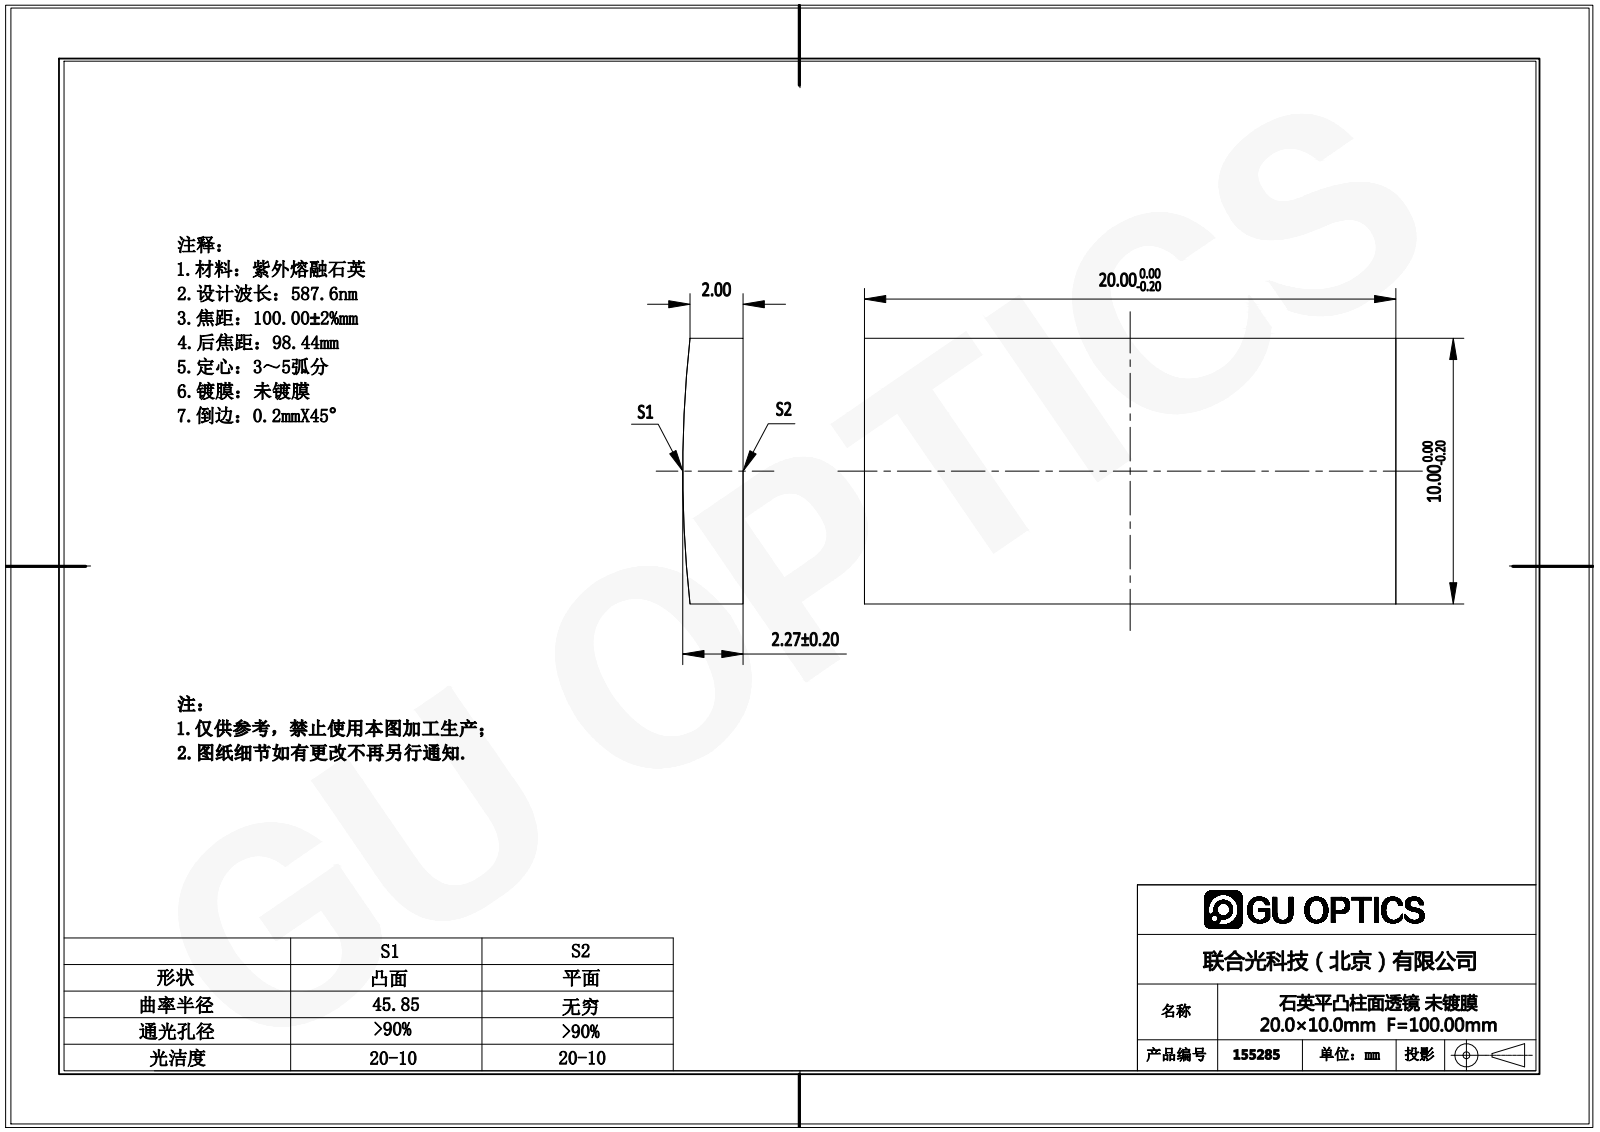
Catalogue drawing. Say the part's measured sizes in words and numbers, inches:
The part is named "155285". Its 3-D file was written by "SolidWorks 2016 (AUTOMOTIVE_DESIGN)". It is 1 solid with 6 faces: 5 planar, 1 cylindrical and 0 other. Overall it measures 0.787 by 0.394 by 0.089 inches. Its volume is 0.027 cubic inches and its surface area 0.812 square inches. Partial cylindrical surfaces (rounded edges, fillets, slot ends): 1 of radius 1.805. The main face-to-face distances are 0.394, 0.787.
